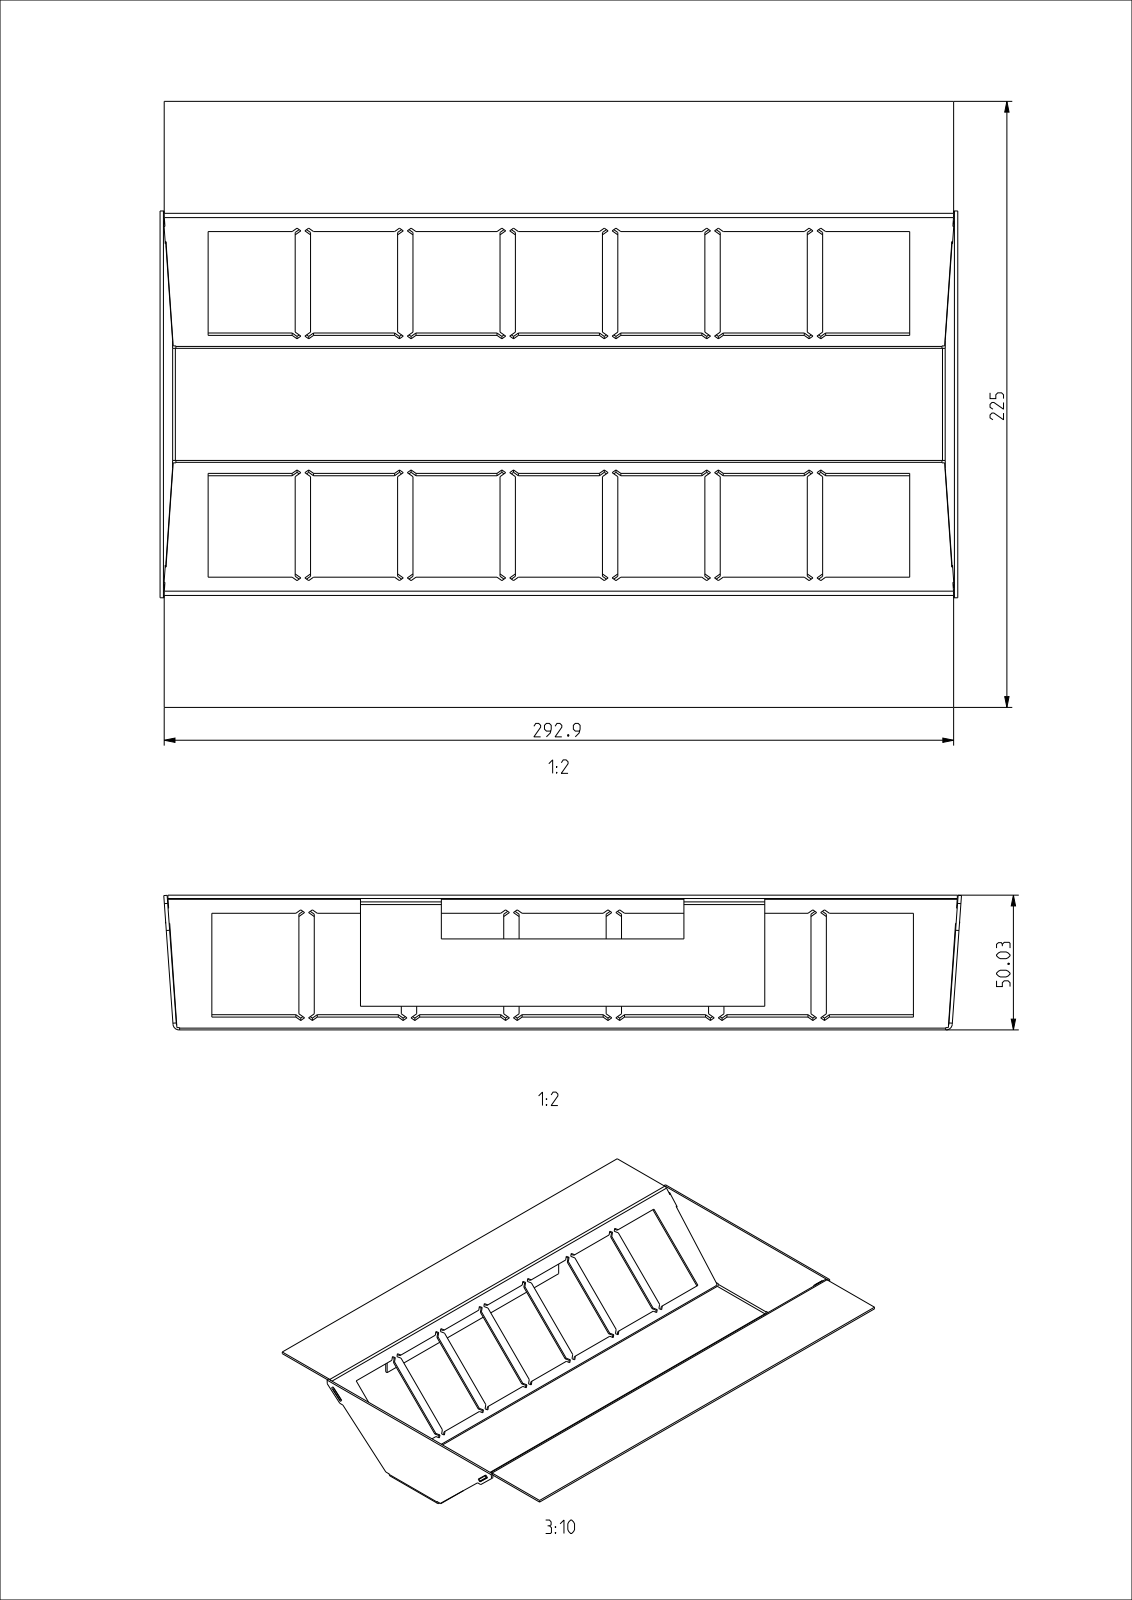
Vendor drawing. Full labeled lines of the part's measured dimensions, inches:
Part name (STEP PRODUCT): T-00643_1; 73700-M_1; T-00642_ASM_1_ASM; T-00832_ASM_1_ASM (+1 more)
STEP written by: CREO PARAMETRIC BY PTC INC, 2022281 (AUTOMOTIVE_DESIGN)
Units: inches
Bodies: 2 solids, 344 faces (324 planar, 16 cylindrical, 4 other)
Overall size (bounding box): 11.652 × 8.858 × 1.97
Volume: 5.099 in³ · Surface area: 216.6 in²
Partial cylindrical surfaces — rounded edges, fillets, slot ends (radius × count): R0.039 ×7, R0.089 ×7
Main face-to-face distances: 0.049, 1.92, 1.871, 1.97, 1.496, 2.992, 4.488, 1.272, 2.768, 5.984
